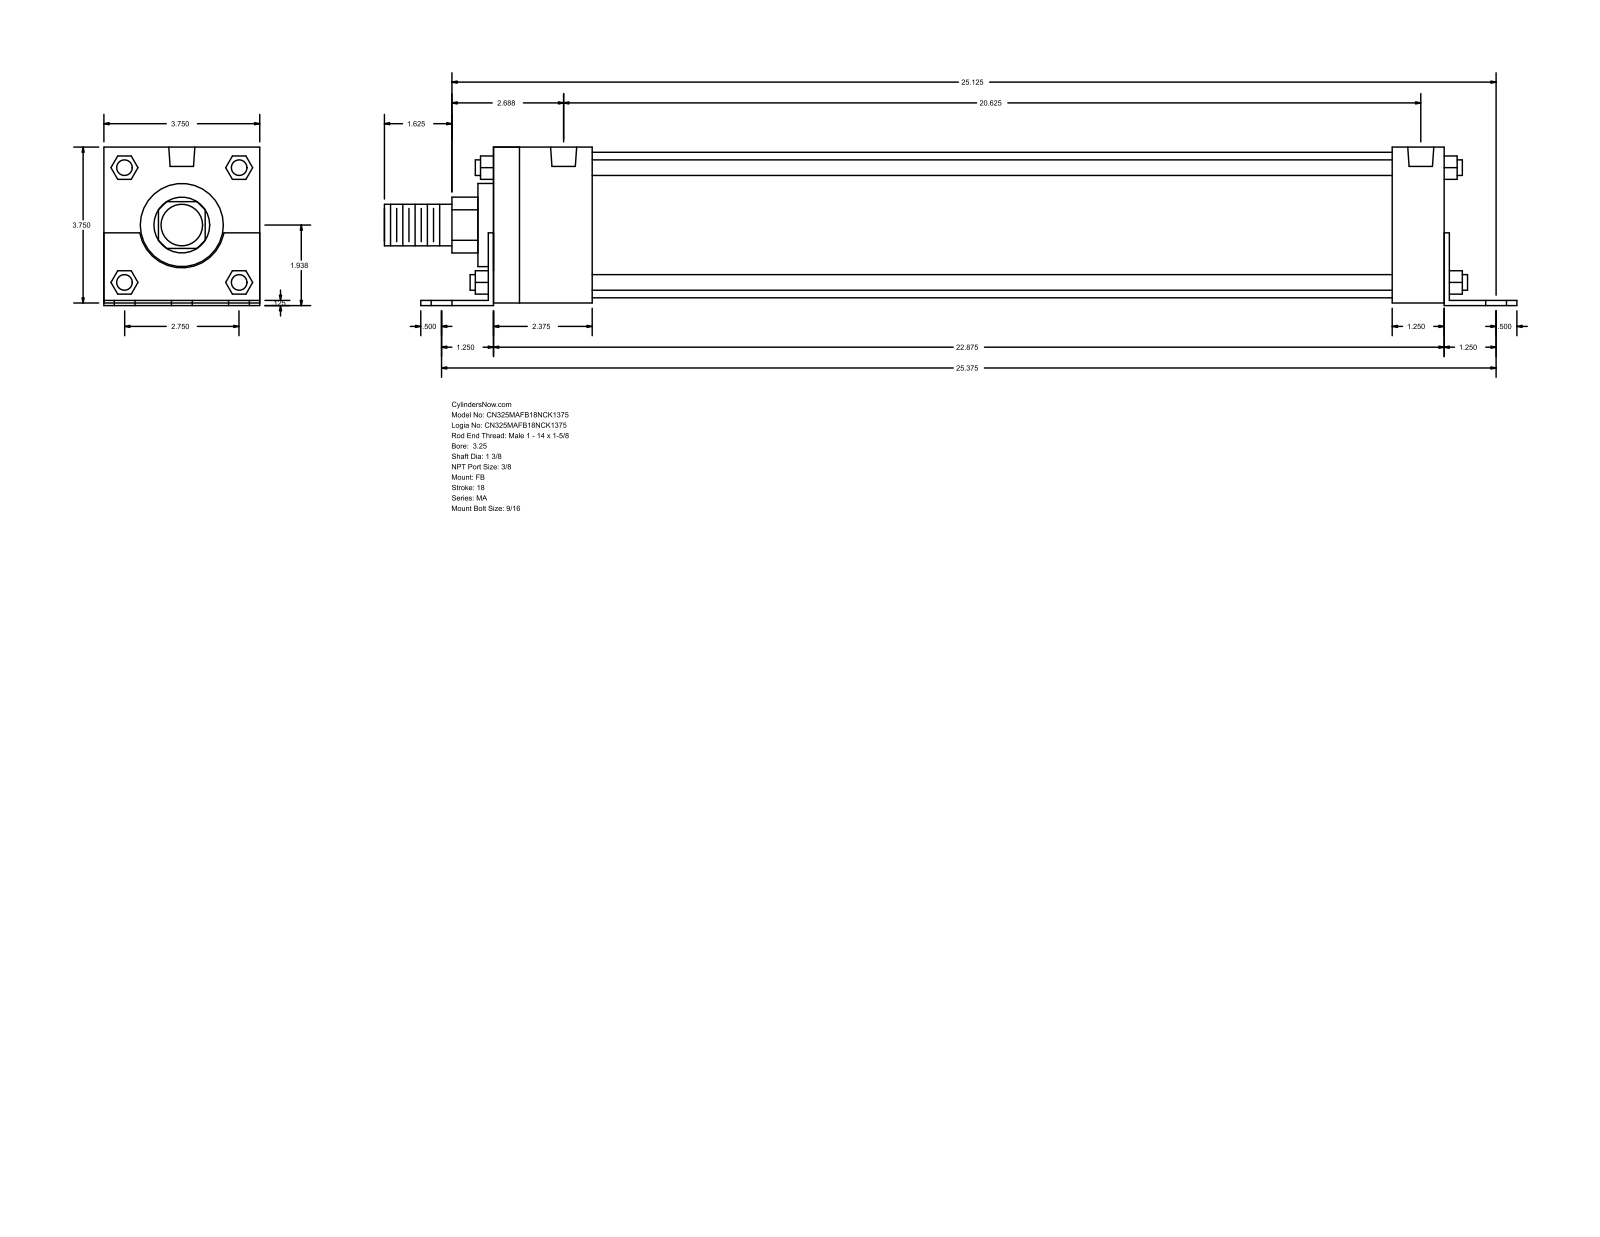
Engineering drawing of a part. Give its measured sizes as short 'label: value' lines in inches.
name: MA_FB__0325_1.375
written by: GSSL Pune (CONFIG_CONTROL_DESIGN)
unit: in
bodies: 0 solids, 140 faces (105 planar, 35 cylindrical, 0 other)
size: 27.25 × 3.813 × 3.75
holes: 6× ⌀0.563, 4× ⌀0.437, 2× ⌀0.627
bosses: 4× ⌀0.375, 1× ⌀3.5, 1× ⌀2, 1× ⌀1.375, 1× ⌀1
rounds: 1× R0.672, 1× R1.03
face distances: 3.75, 0.125, 0.063, 3.812, 0.062, 3.687, 0.125, 22.875, 23, 1.25
hole spacings: 1.375, 25.412, 25.375, 2.275, 2.427, 2.75, 3.243, 3.414
